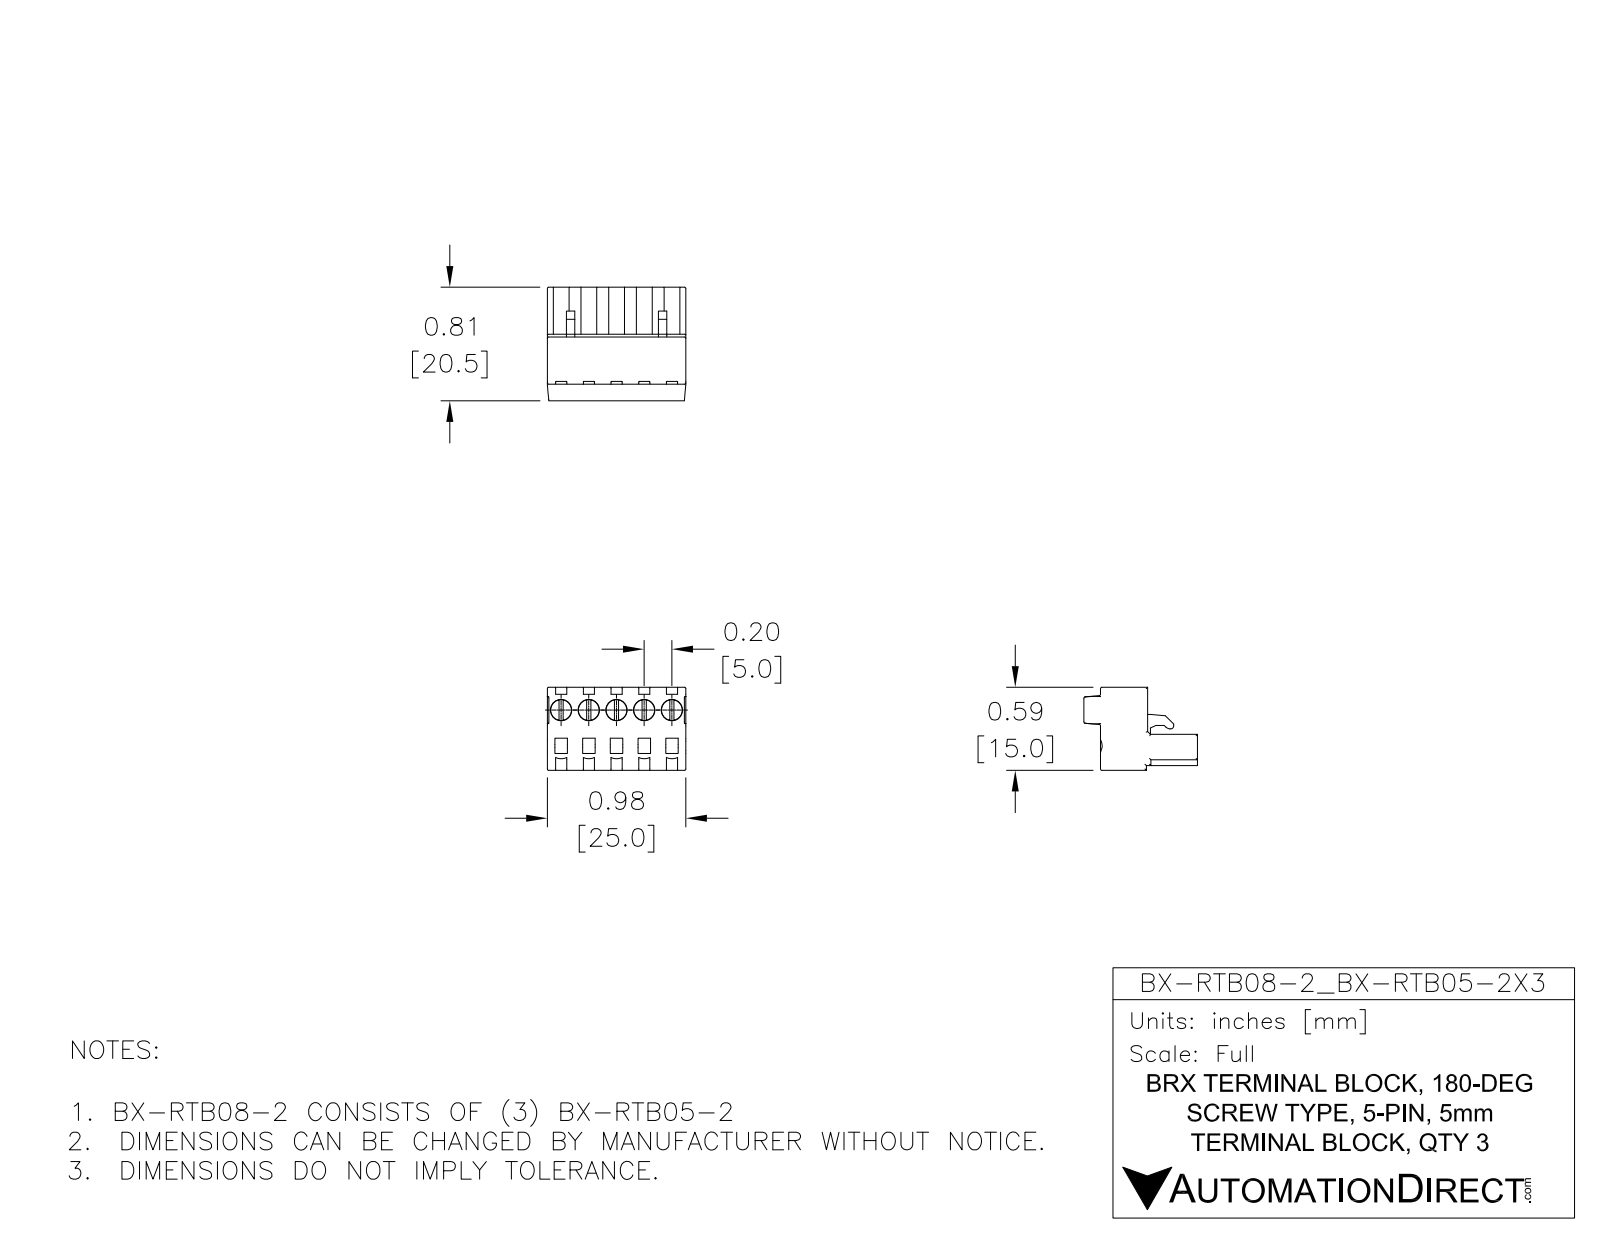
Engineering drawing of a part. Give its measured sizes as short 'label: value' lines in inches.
name: BX-RTB08-2
written by: SolidWorks 2017 (AUTOMOTIVE_DESIGN)
unit: in
bodies: 3 solids, 1116 faces (621 planar, 306 cylindrical, 189 other)
size: 3.953 × 0.807 × 0.591
volume: 0.768 in³; area: 14.47 in²
holes: 15× ⌀0.063, 15× ⌀0.124, 15× ⌀0.152
bosses: 15× ⌀0.148
rounds: 90× R0.01, 15× R0.092, 15× R0.099, 1× R0.02, 1× R0.039
face distances: 1.484, 0.335, 0.591, 0.984, 0.224, 0.366, 2.969, 0.5, 2.469, 0.354
hole spacings: 0.197, 1.484, 0.394, 1.287, 1.681, 0.295, 0.354, 0.355
